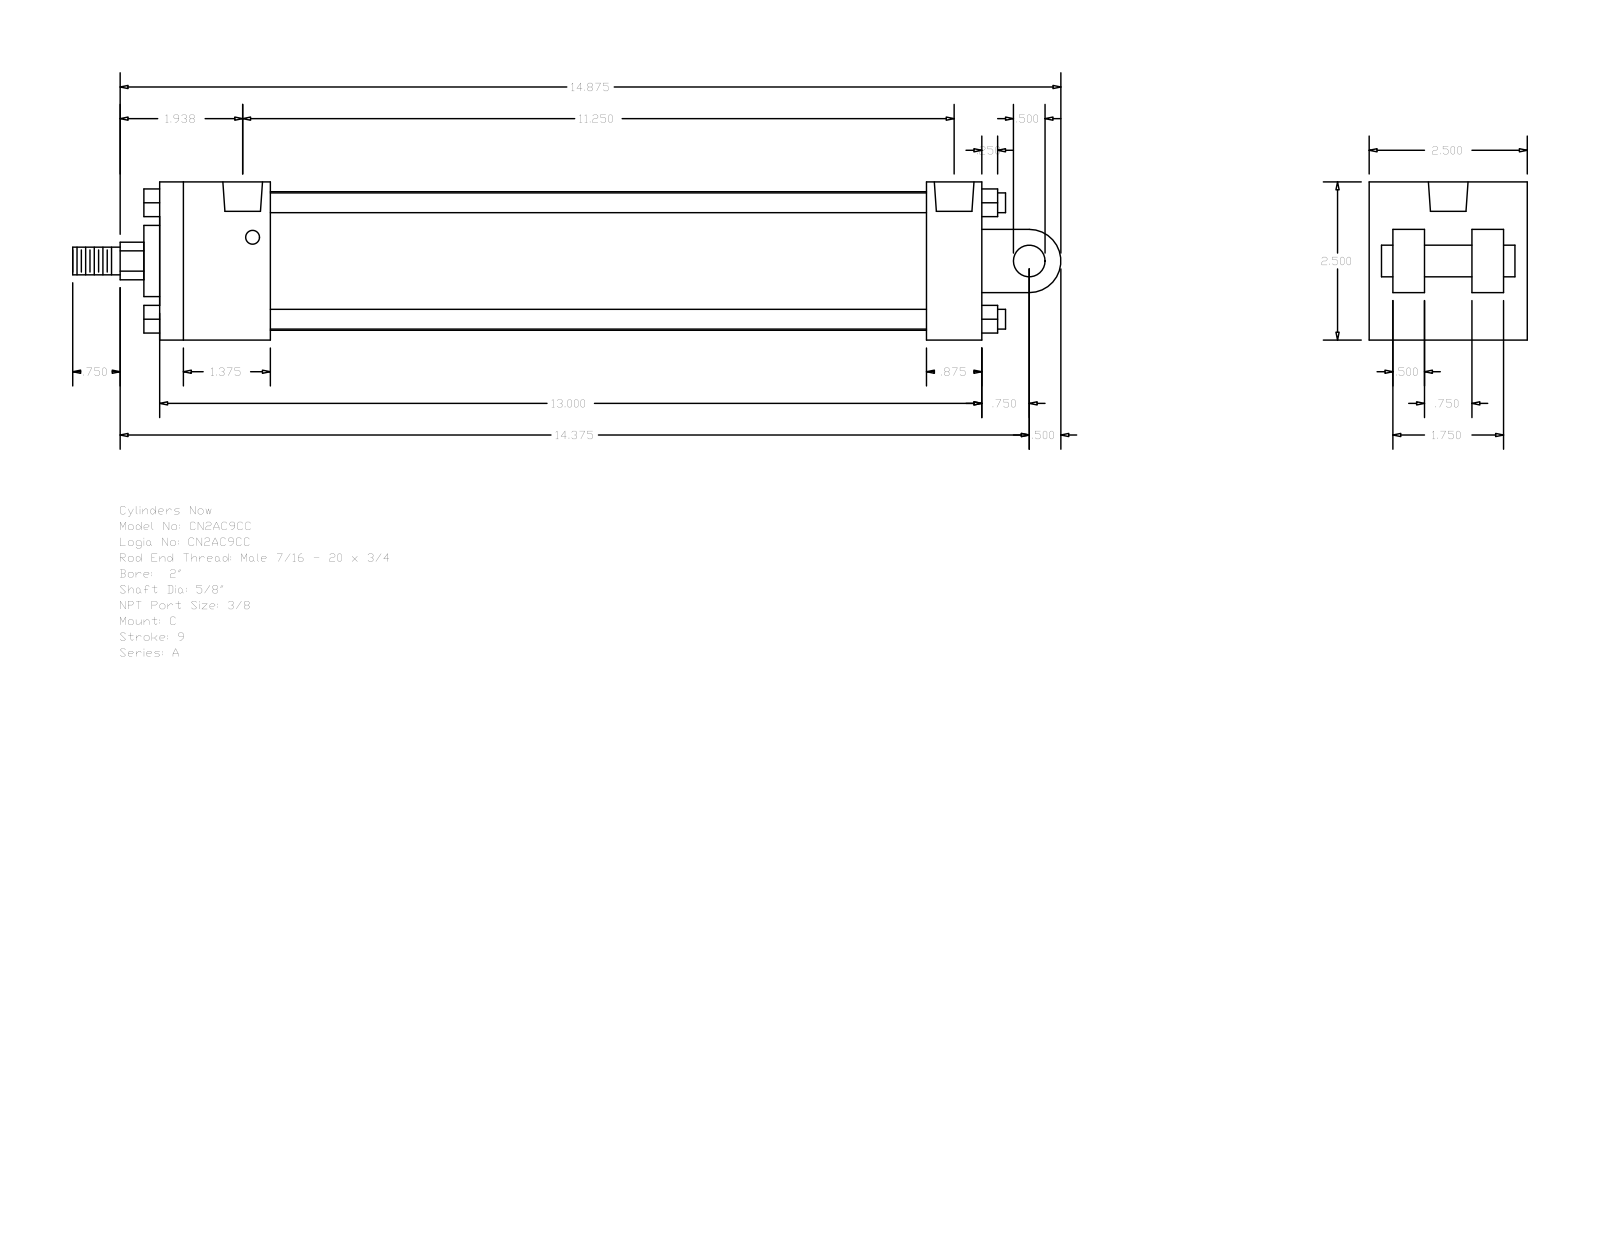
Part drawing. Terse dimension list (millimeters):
name: A_C__0200_0.625
written by: GSSL Pune (CONFIG_CONTROL_DESIGN)
unit: mm
bodies: 0 solids, 135 faces (102 planar, 33 cylindrical, 0 other)
size: 396.88 × 63.5 × 63.5
holes: 4× ⌀5.56, 2× ⌀15.93
bosses: 4× ⌀7.94, 1× ⌀55.63, 1× ⌀28.57, 1× ⌀15.88, 1× ⌀12.7, 1× ⌀11.11
rounds: 1× R7.54, 1× R12.7
face distances: 63.5, 330.19, 22.22, 44.45, 285.74, 307.97, 263.52, 12.7, 53.98, 19.05
hole spacings: 277.8, 3.97, 3.98, 281.77, 281.78, 285.75
